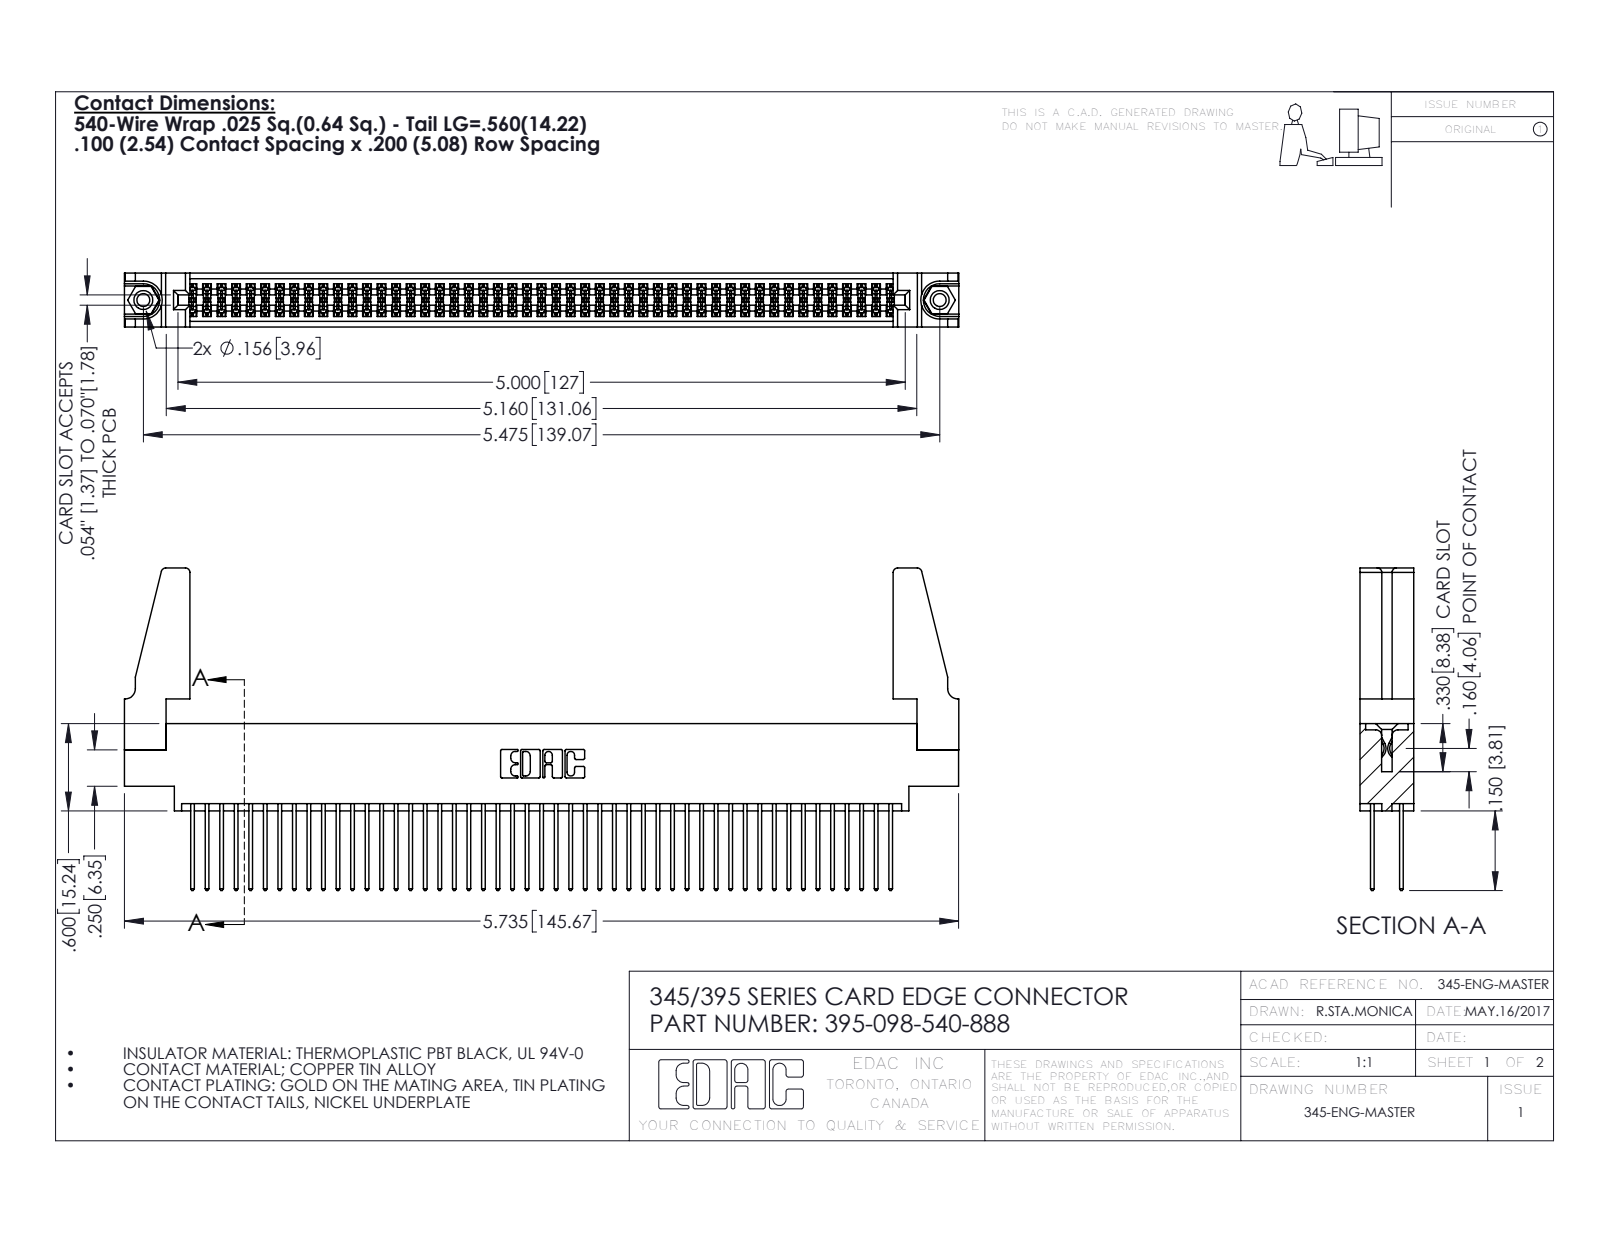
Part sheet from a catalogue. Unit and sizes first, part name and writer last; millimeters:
Units: millimetres
Overall size (bounding box): 145.7 × 56.3 × 9.4
Round holes (diameter × count): ⌀2.3 ×2, ⌀3.2 ×2, ⌀4 ×2, ⌀1.6 ×1
Round bosses / shafts (diameter × count): ⌀3.9 ×2
Partial cylindrical surfaces — rounded edges, fillets, slot ends (radius × count): R0.2 ×147, R0.3 ×98, R0.3 ×22, R0.8 ×8, R0.2 ×6, R0.8 ×6, R0.7 ×3, R0.4 ×2
Main face-to-face distances: 1.8, 7.6, 9.4, 2.5, 6.9, 0.6, 5.1, 5.7, 4.4, 3.8
Hole centre spacings: 6.9, 133.1, 139.1
Volume: 17 730 mm³ · Surface area: 26 520 mm²
Bodies: 103 solids, 5154 faces (3390 planar, 1748 cylindrical, 16 other)
Part name (STEP PRODUCT): 345 Part_0.170 Offset - 0.156 Dia-TH; 345-220-078_345-220-088; 395-098-540-888; 345-250-001_345-250-001-102 (+1 more)
STEP written by: SolidWorks 2016 (CONFIG_CONTROL_DESIGN)
